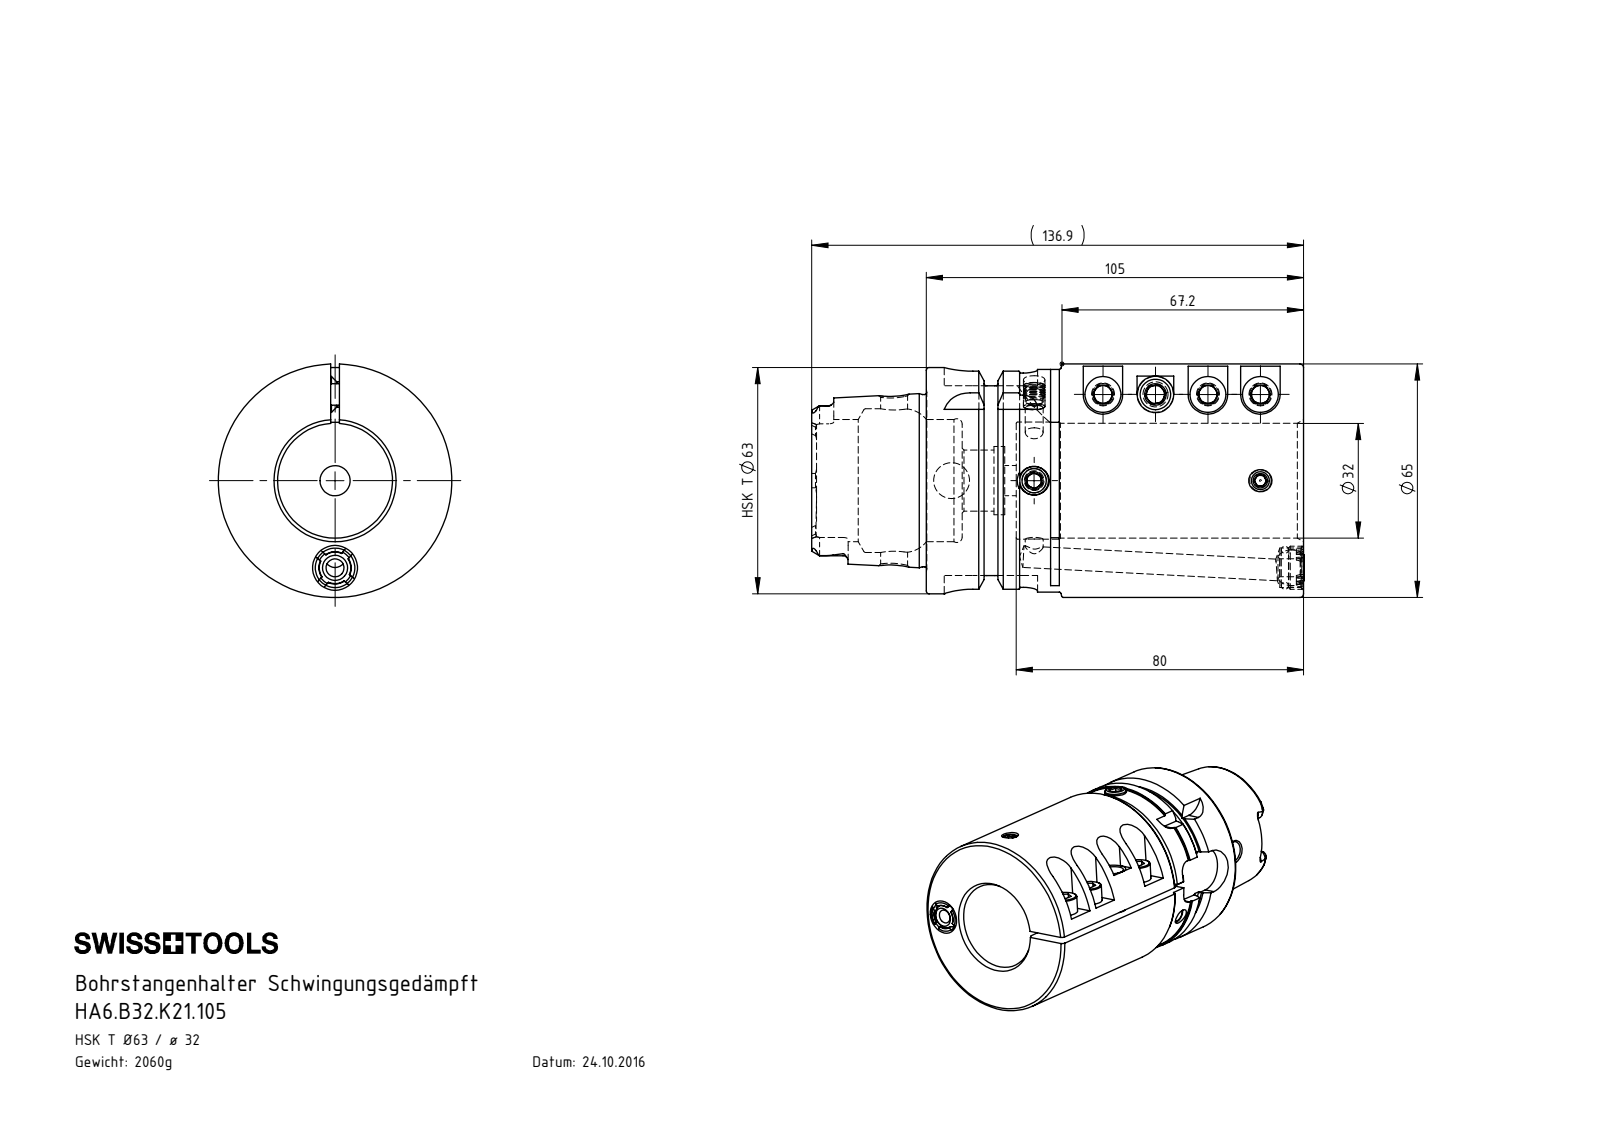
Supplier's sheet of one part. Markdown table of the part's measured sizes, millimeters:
| quantity | value |
| --- | --- |
| part name | ISO 4028 - M10 x 16; ISO 4762 - M6 x 16_PreviewCfg; HA6-B32.K21.105_A; DIN 3771 - 8x1.5 (+7 more) |
| STEP written by | SolidWorks 2017 (AUTOMOTIVE_DESIGN) |
| units | millimeters |
| bodies | 12 solids, 630 faces (181 planar, 222 cylindrical, 227 other) |
| overall size | 137.38 × 65 × 64.98 |
| volume | 262 156 mm³ |
| surface area | 60 339 mm² |
| round holes (diameter × count) | 5 × 7, 6.4 × 3, 6 × 2, 10 × 2, 4 × 1, 6.8 × 1, 7.5 × 1, 8.4 × 1, 8.5 × 1, 11 × 1, 17 × 1, 19 × 1 |
| round bosses / shafts (diameter × count) | 6 × 5, 10 × 4, 65 × 1, 63 × 1, 62 × 1, 54.95 × 1, 47.94 × 1, 12 × 1 |
| partial cylindrical surfaces (radius × count) | 1.4 × 6, 4 × 5, 2.88 × 4, 8 × 4, 5.5 × 3, 4.4 × 1, 5.1 × 1, 52 × 1 |
| main face-to-face distances | 2.4, 68, 70.4, 34.6, 37, 105, 25, 9.6, 12, 80 |
| hole center spacings | 14.61, 29.22, 23, 24, 24.25, 28.1, 30.72, 37.81 |
